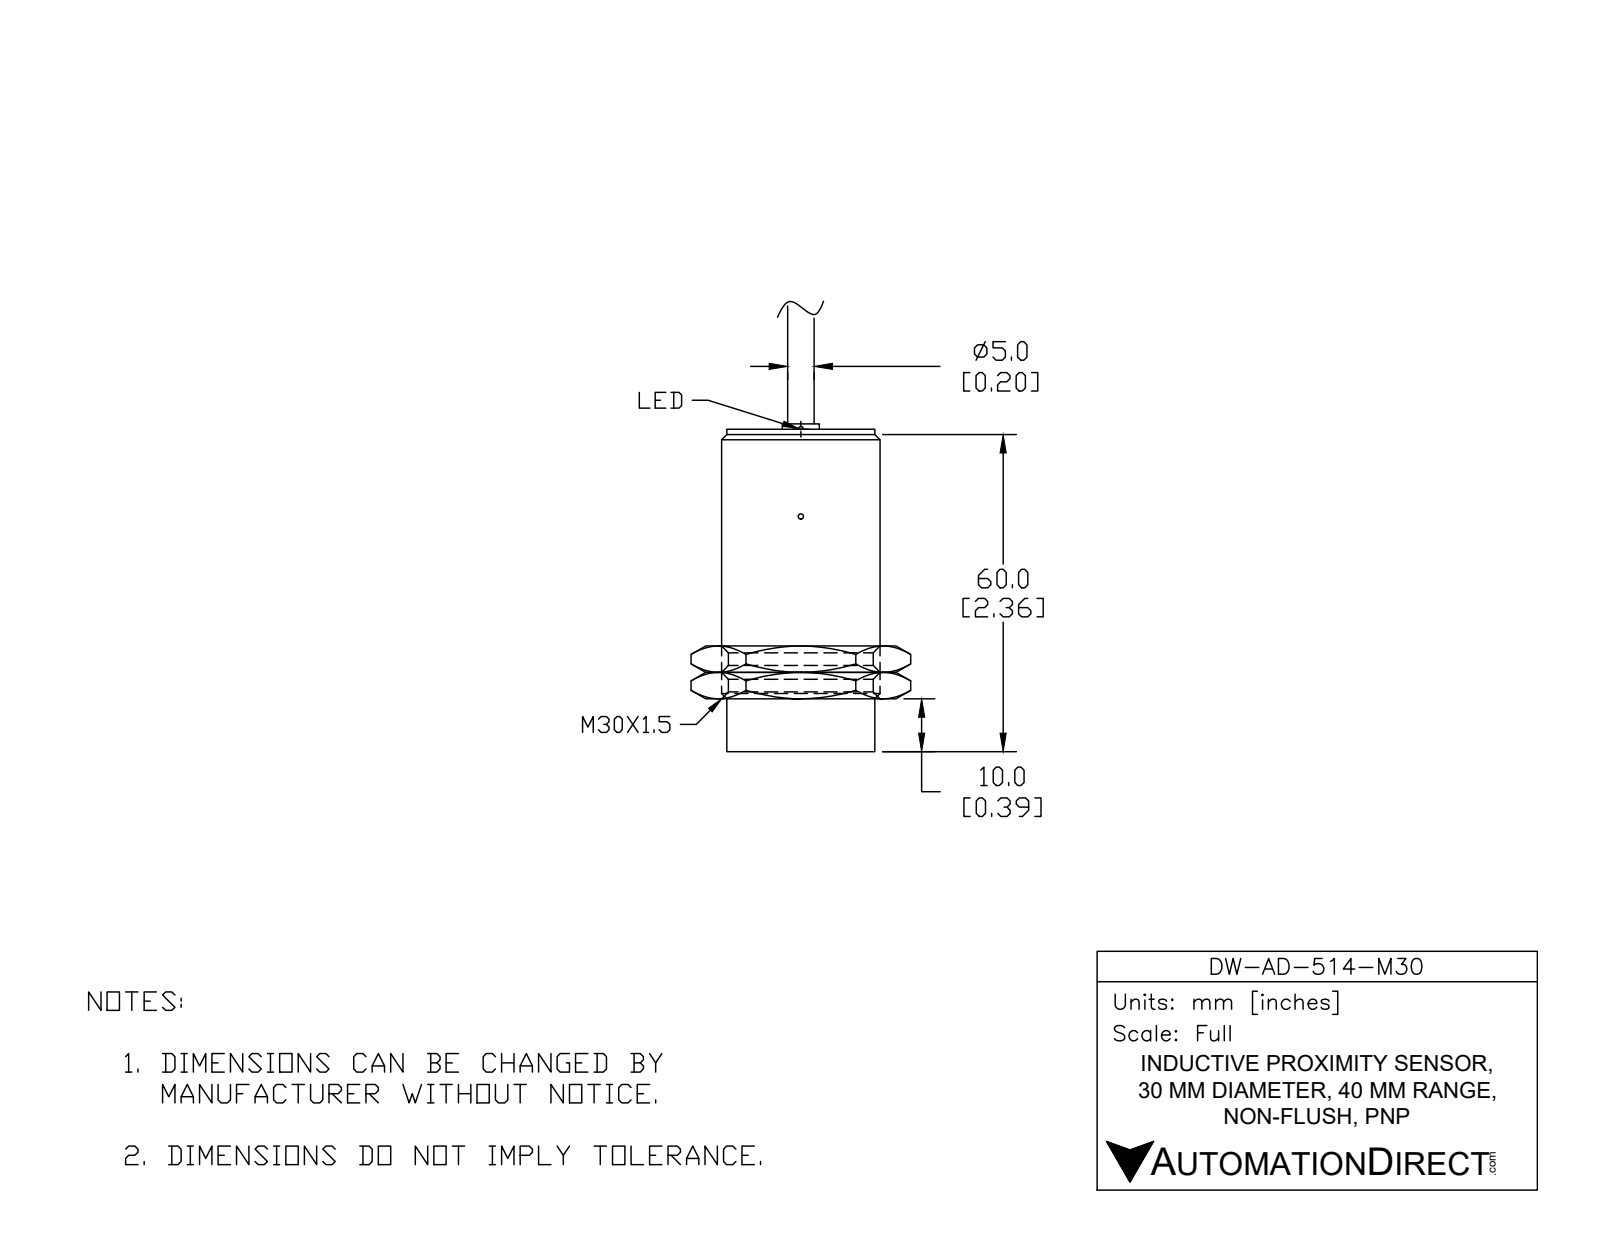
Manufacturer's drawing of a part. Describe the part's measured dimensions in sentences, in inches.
The part is named "DW-AD-514-M30". Its 3-D file was written by "SolidWorks 2017 (AUTOMOTIVE_DESIGN)". It is 2 solids with 16 faces: 6 planar, 4 cylindrical and 6 other. Overall it measures 3.465 by 1.181 by 1.181 inches. Its volume is 2.596 cubic inches and its surface area 13.34 square inches. Round bosses or shafts: 1 of diameter 1.181, 1 of diameter 1.083, 1 of diameter 0.413, 1 of diameter 0.197. The main face-to-face distances are 0.394, 2.402, 2.008, 2.431, 2.038, 0.03, 3.465, 3.071, 1.063, 1.033.
